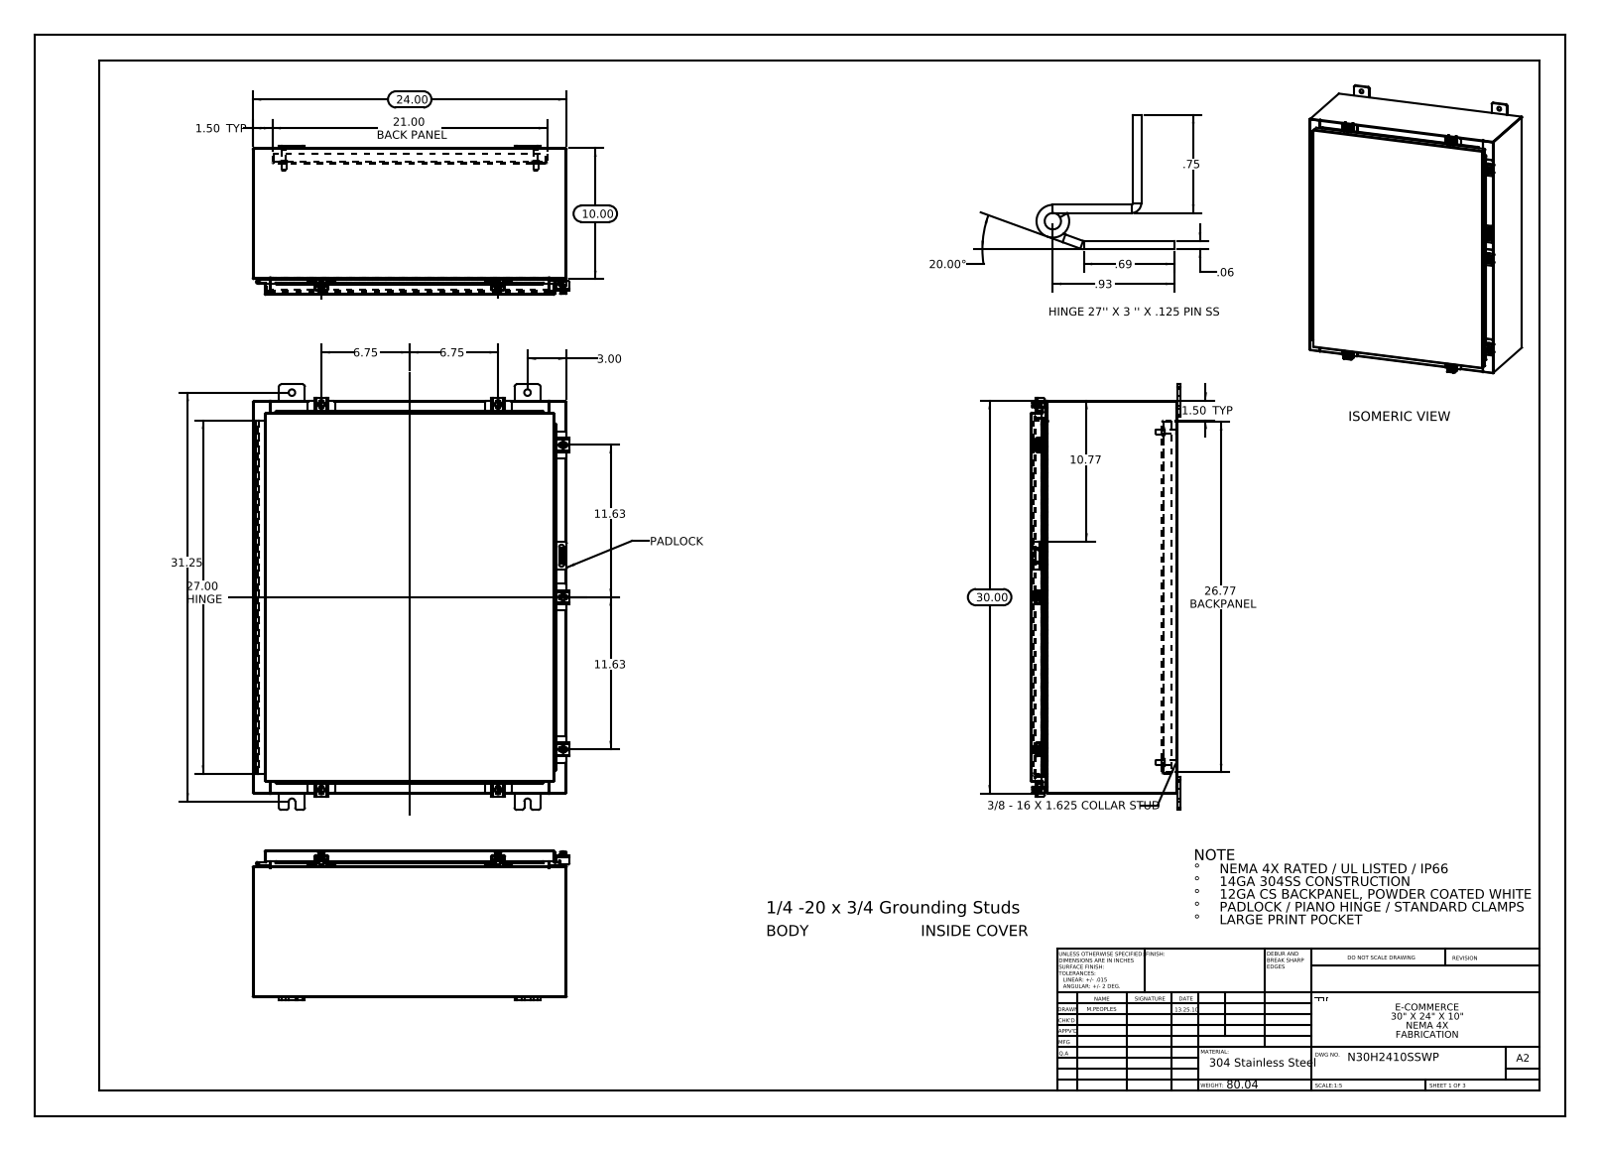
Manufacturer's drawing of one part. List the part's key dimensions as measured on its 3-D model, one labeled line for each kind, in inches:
Part name (STEP PRODUCT): N30H2410SSWP Hinge Enclosure Side2; N30H2410SSWP 125 Pin Hinge; N30H2410SSWP Padlock Hasp; N30H2410SSWP Bottom (+8 more)
STEP written by: SolidWorks 2013 (CONFIG_CONTROL_DESIGN)
Units: inches
Bodies: 52 solids, 1990 faces (1056 planar, 830 cylindrical, 104 other)
Overall size (bounding box): 32.5 × 24.211 × 11.389
Volume: 280.9 in³ · Surface area: 7 049 in²
Round holes (diameter × count): ⌀0.5 ×8, ⌀0.213 ×7, ⌀0.26 ×7, ⌀0.125 ×2, ⌀0.125 ×1
Round bosses / shafts (diameter × count): ⌀0.25 ×8, ⌀0.5 ×7, ⌀0.399 ×7, ⌀0.625 ×4, ⌀0.375 ×4, ⌀0.33 ×4
Partial cylindrical surfaces — rounded edges, fillets, slot ends (radius × count): R0.06 ×34, R0.013 ×27, R0.19 ×24, R0.088 ×21, R0.12 ×14, R0.141 ×14, R0.05 ×11, R0.08 ×10
Main face-to-face distances: 0.075, 11.126, 11.201, 11.051, 0.104, 23.925, 1, 1.075, 10.051, 10.126
Hole centre spacings: 27.501, 31.878, 1.858, 2.277, 2.326, 2.423, 3.561, 3.561
